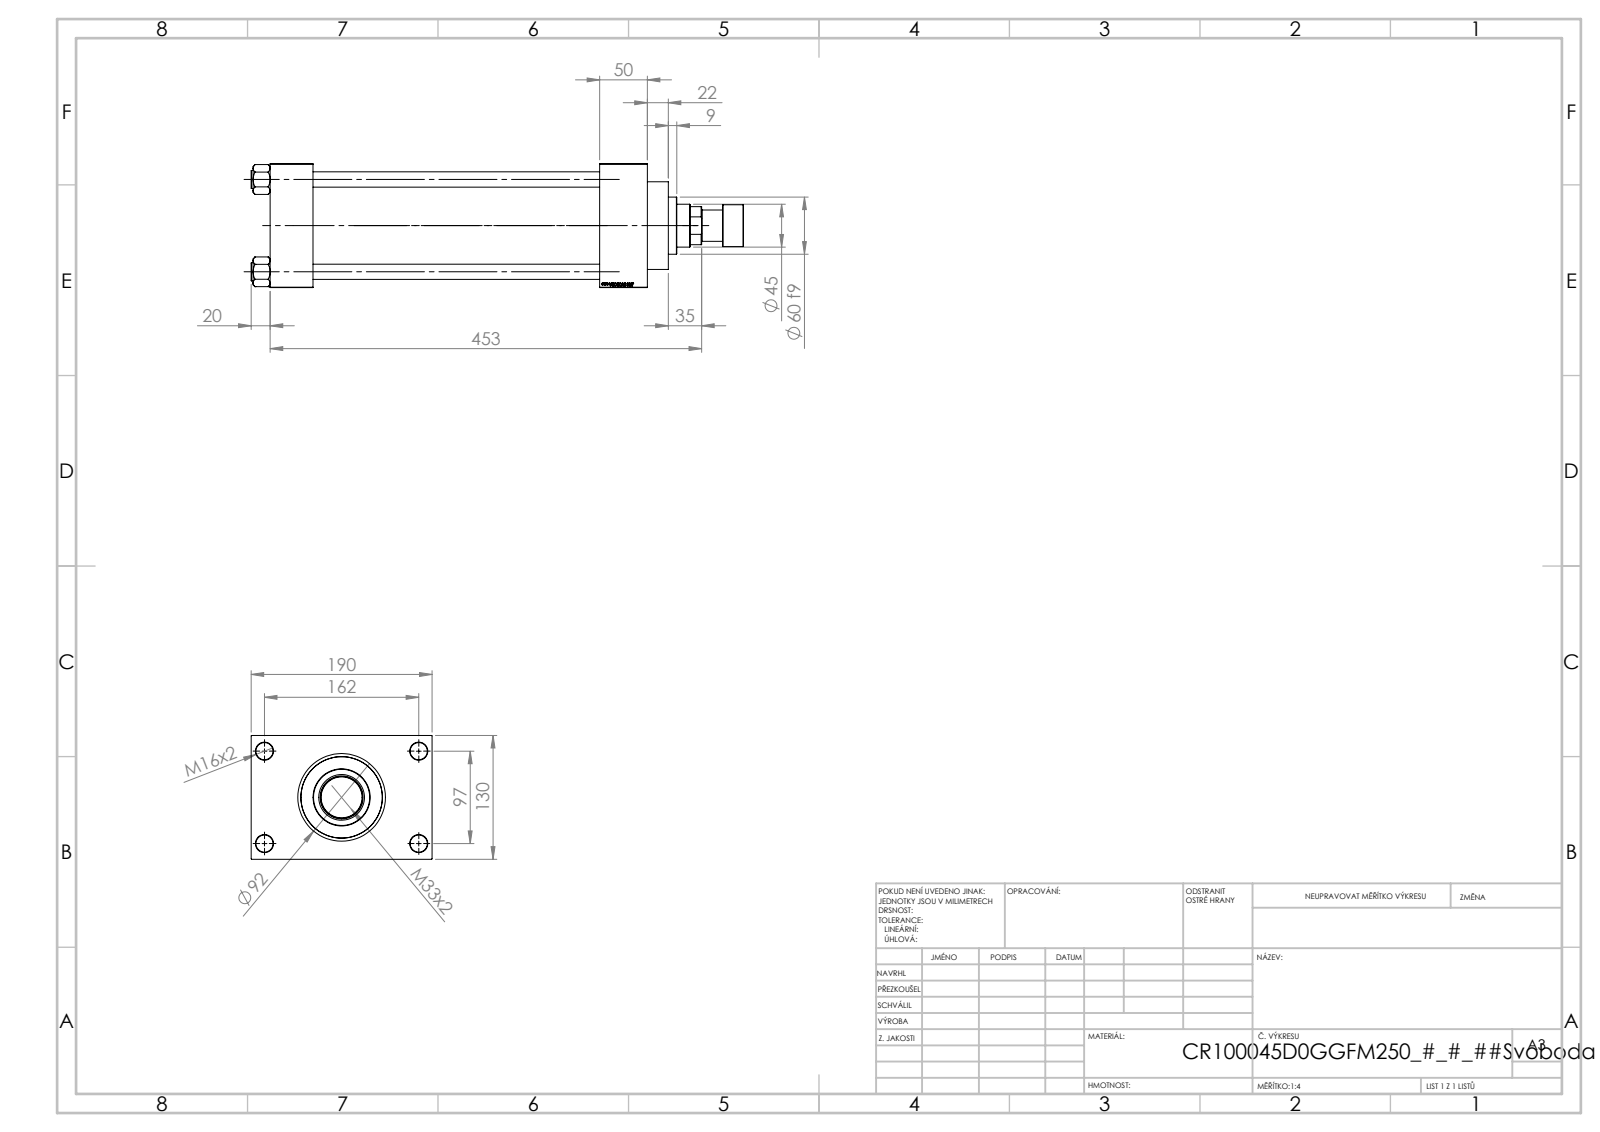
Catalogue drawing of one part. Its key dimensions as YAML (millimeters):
part_name: "V215_VC_A; V215CR_D_TYCINKA; V215CR_D_Body; V215CR_ROD_END_F (+2 more)"
step_written_by: "SolidWorks 2019 (CONFIG_CONTROL_DESIGN)"
units: millimeters
bodies: {solids: 12, faces: 1165, planar: 548, cylindrical: 93, other: 524}
overall_size: [517, 190, 130]
volume: 3433000
surface_area: 588381
round_holes:
  - {diameter: 16, count: 4}
  - {diameter: 18, count: 4}
  - {diameter: 7, count: 2}
  - {diameter: 26.44, count: 2}
  - {diameter: 35, count: 2}
  - {diameter: 31.5, count: 1}
  - {diameter: 45, count: 1}
  - {diameter: 48, count: 1}
  - {diameter: 76, count: 1}
  - {diameter: 85.5, count: 1}
  - {diameter: 100, count: 1}
round_bosses_or_shafts:
  - {diameter: 19, count: 4}
  - {diameter: 106, count: 1}
  - {diameter: 92, count: 1}
  - {diameter: 60, count: 1}
  - {diameter: 44, count: 1}
  - {diameter: 33, count: 1}
face_to_face_distances: [130, 45, 346, 301, 396, 351, 50, 30, 160, 190]
hole_center_spacings: [32.55, 68.52, 94.41, 96.9, 102.27, 129.45, 161.73, 97]
